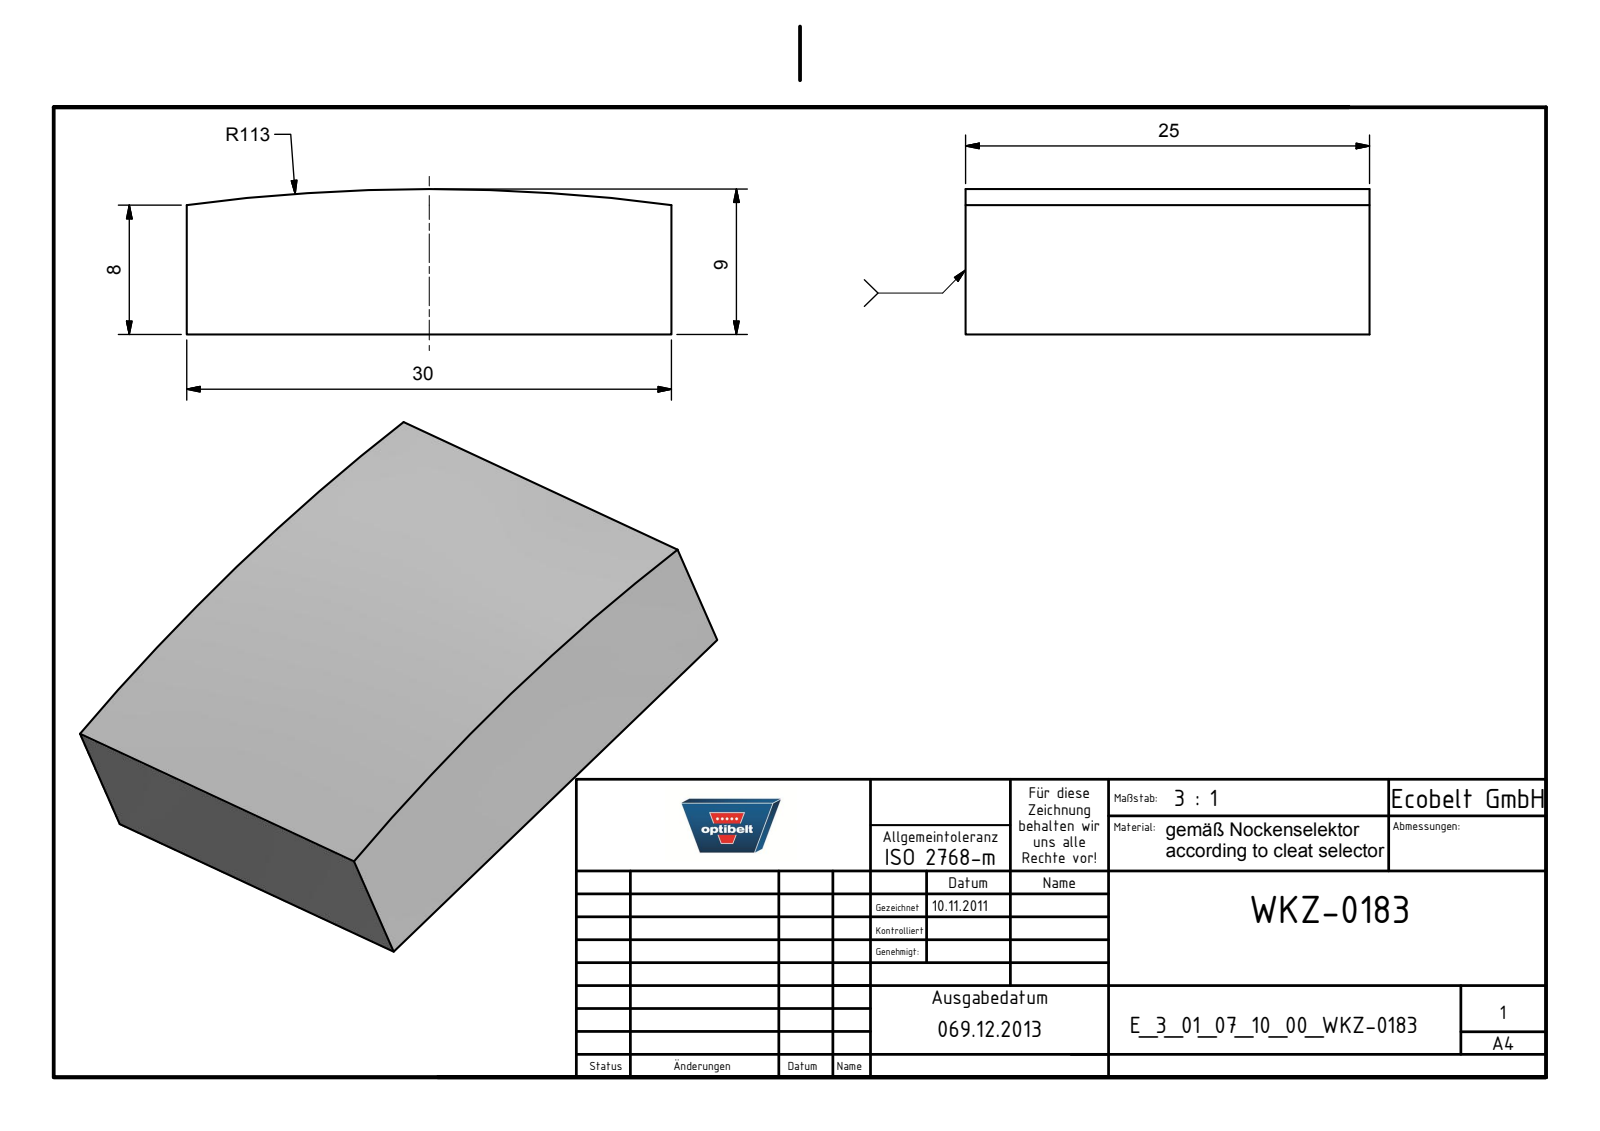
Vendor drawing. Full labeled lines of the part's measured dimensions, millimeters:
Part name (STEP PRODUCT): E_3_01_07_10_00_WKZ-0183
STEP written by: Autodesk Inventor 2025 (AUTOMOTIVE_DESIGN)
Units: millimetres
Bodies: 1 solid, 6 faces (5 planar, 1 cylindrical, 0 other)
Overall size (bounding box): 30 × 25 × 9
Volume: 6 500 mm³ · Surface area: 2 422 mm²
Partial cylindrical surfaces — rounded edges, fillets, slot ends (radius × count): R113 ×1
Main face-to-face distances: 25, 30
